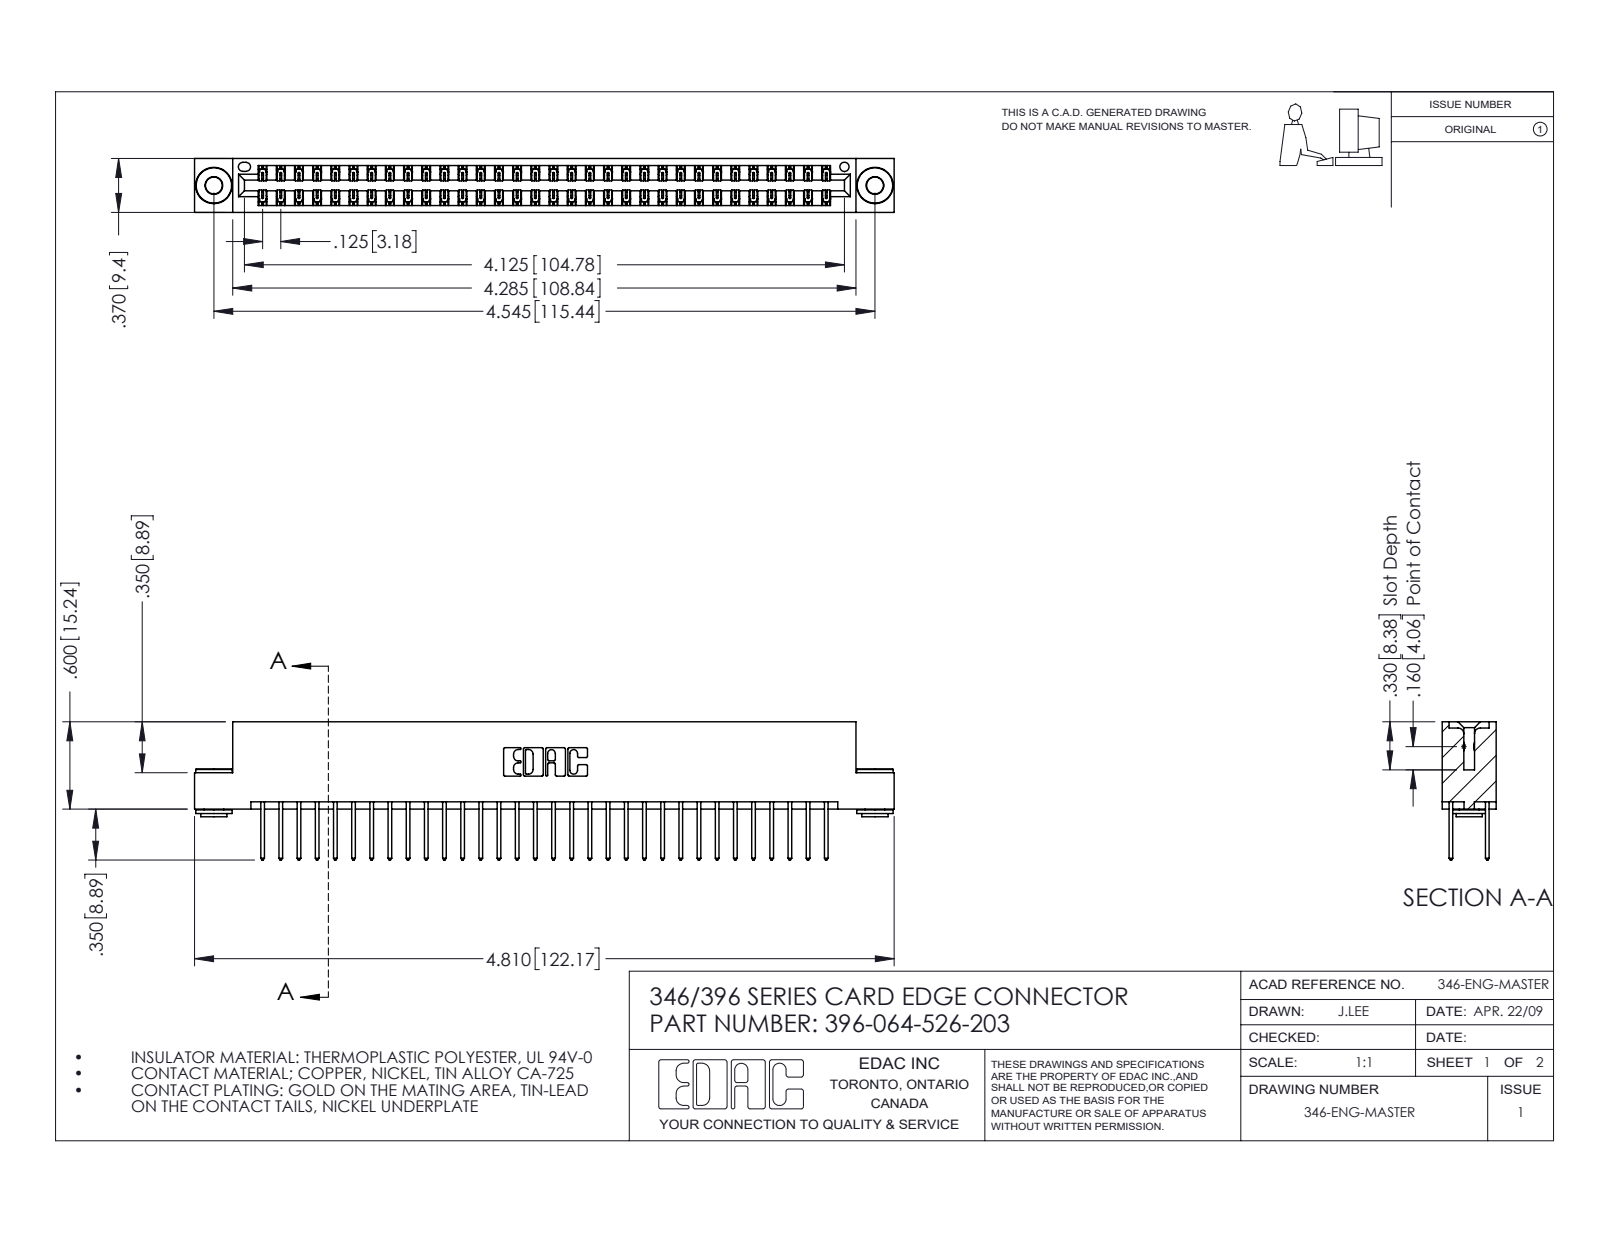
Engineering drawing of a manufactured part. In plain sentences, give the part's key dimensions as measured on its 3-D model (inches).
The part is named "346 Part_Flush Mounting Lugs - 0.156 Dia-TH; 396-064-526-203; 345-250-002_345-250-002-102; 345-292-001_345-293-126". Its 3-D file was written by "SolidWorks 2016 (CONFIG_CONTROL_DESIGN)". It is 67 solids with 3488 faces: 2326 planar, 1154 cylindrical and 8 other. Overall it measures 4.81 by 0.95 by 0.37 inches. Its volume is 0.73 cubic inches and its surface area 26.3 square inches. Round holes: 2 of diameter 0.116, 2 of diameter 0.156, 1 of diameter 0.064. Round bosses or shafts: 2 of diameter 0.25, 2 of diameter 0.18, 2 of diameter 0.136. Partial cylindrical surfaces (rounded edges, fillets, slot ends): 96 of radius 0.006, 64 of radius 0.01, 22 of radius 0.01, 6 of radius 0.007, 6 of radius 0.031, 3 of radius 0.026, 2 of radius 0.014, 2 of radius 0.022. The main face-to-face distances are 0.048, 0.322, 0.25, 0.37, 0.025, 0.072, 0.298, 0.275, 0.148, 0.222. The hole center spacings are 0.246, 4.337, 4.545.
